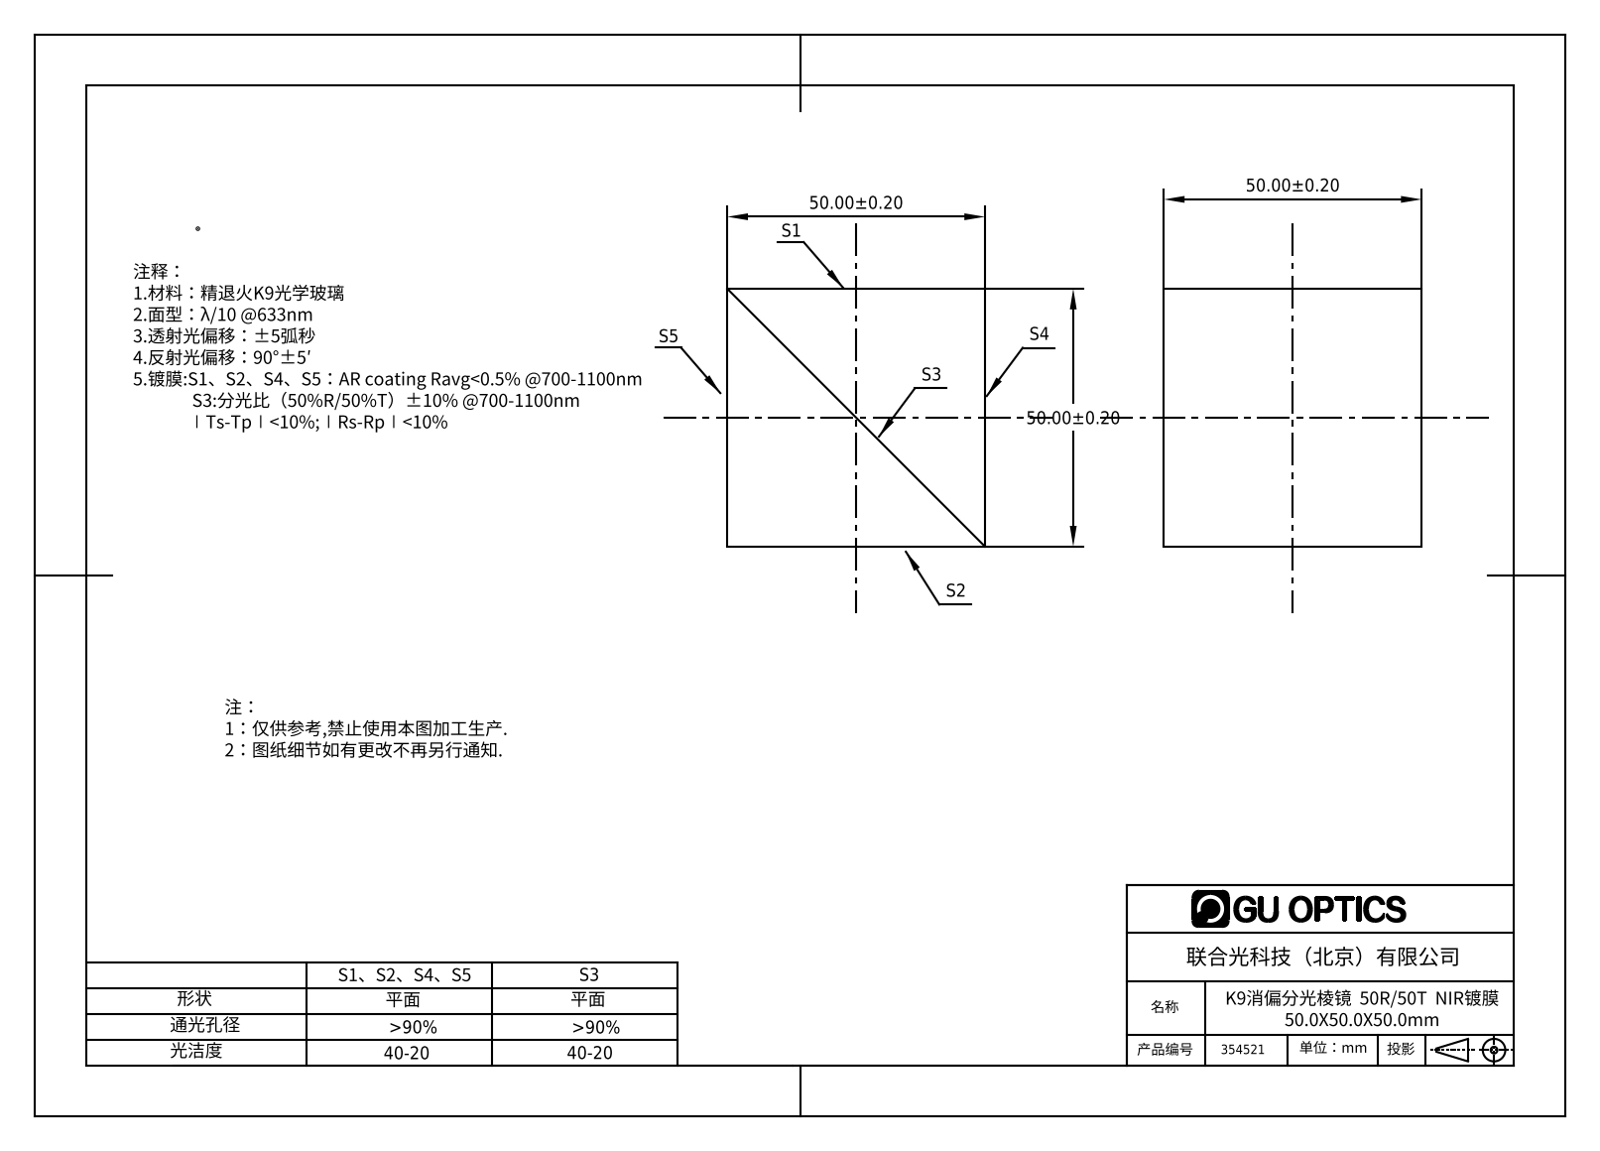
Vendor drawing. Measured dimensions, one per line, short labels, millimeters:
name: 354510
written by: SolidWorks 2016 (AUTOMOTIVE_DESIGN)
unit: mm
bodies: 2 solids, 10 faces (10 planar, 0 cylindrical, 0 other)
size: 50 × 50 × 50
volume: 125 000 mm³; area: 22 071 mm²
face distances: 50
